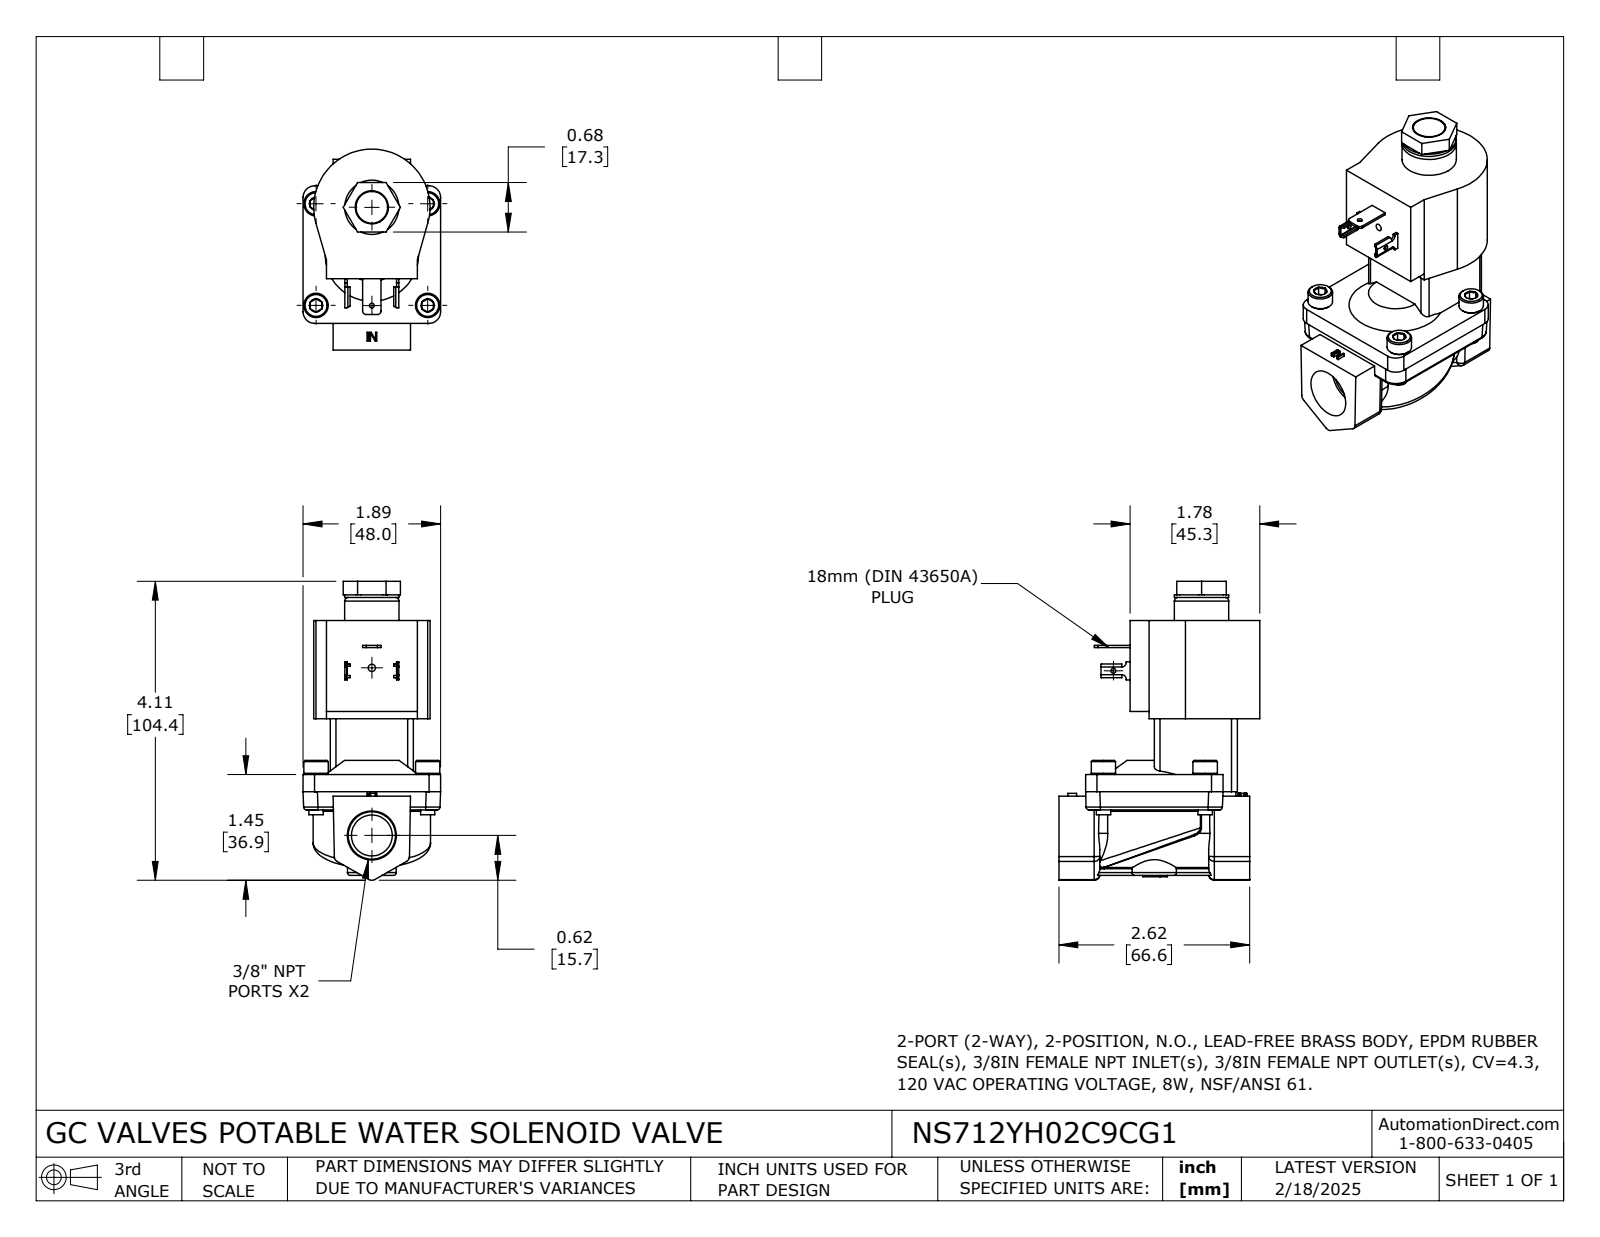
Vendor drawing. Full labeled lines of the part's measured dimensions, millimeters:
Part name (STEP PRODUCT): NS712YH02C9CG1
STEP written by: SolidWorks 2024 (CONFIG_CONTROL_DESIGN)
Units: millimetres
Bodies: 2 solids, 501 faces (276 planar, 118 cylindrical, 107 other)
Overall size (bounding box): 104.4 × 70.12 × 48
Volume: 137 697 mm³ · Surface area: 25 960 mm²
Round holes (diameter × count): ⌀1.68 ×1, ⌀1.7 ×1, ⌀2.53 ×1, ⌀11.58 ×1, ⌀14.27 ×1, ⌀30.48 ×1
Round bosses / shafts (diameter × count): ⌀8.5 ×4, ⌀5 ×4, ⌀18.95 ×1
Partial cylindrical surfaces — rounded edges, fillets, slot ends (radius × count): R2 ×15, R0.5 ×6, R1 ×6, R0.15 ×4, R1.04 ×4, R4 ×4, R5 ×4, R1.27 ×2
Main face-to-face distances: 53.79, 29, 33.3, 37.44, 19.5, 34.29, 9.5, 27, 38.5, 41.74
Hole centre spacings: 34.29, 58.5
